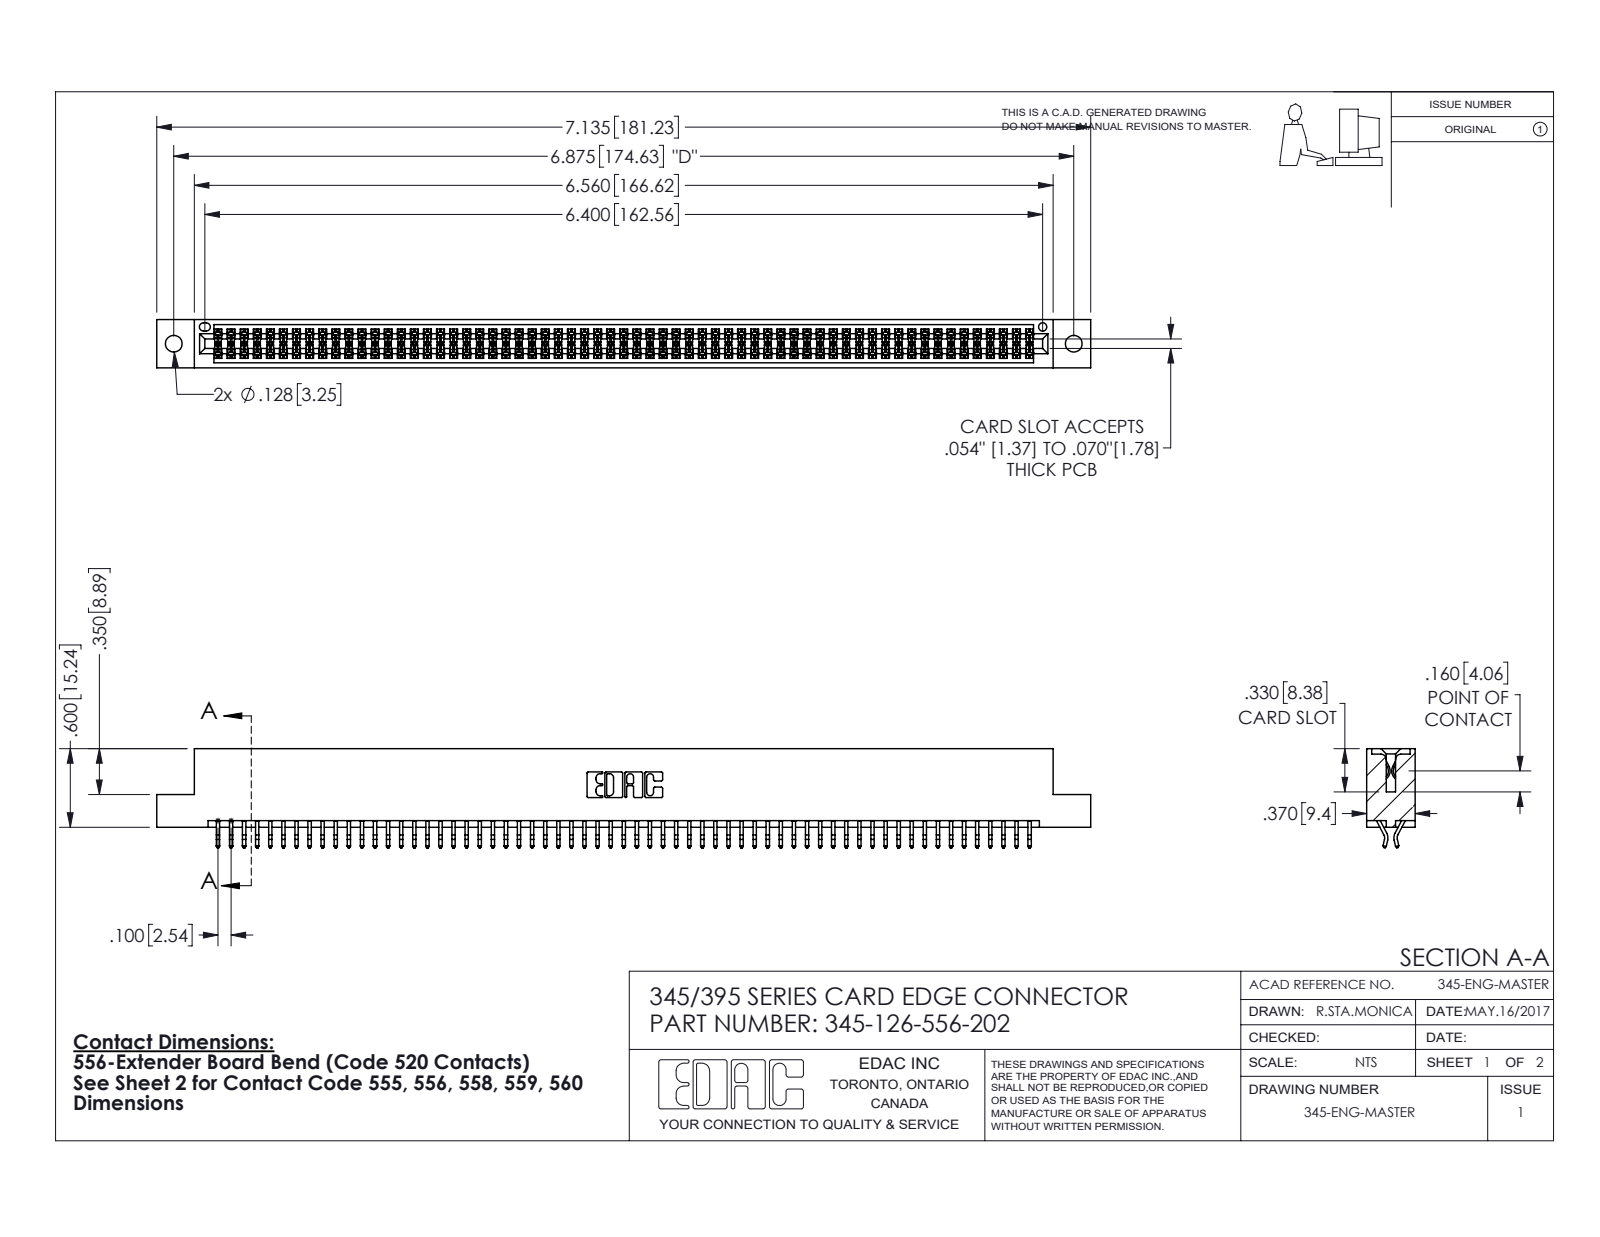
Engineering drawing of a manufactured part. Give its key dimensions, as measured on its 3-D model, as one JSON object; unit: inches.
{"part_name": "345-126-556-202; 345 Part_Flush Mounting Lugs - 0.128 Dia; 345-292-001_556 Tail", "step_written_by": "SolidWorks 2016 (CONFIG_CONTROL_DESIGN)", "units": "inches", "bodies": {"solids": 127, "faces": 7182, "planar": 4742, "cylindrical": 2440, "other": 0}, "overall_size": [7.135, 0.757, 0.37], "volume_in3": 1.084, "surface_area_in2": 40.72, "round_holes": [[0.128, 2], [0.064, 1]], "partial_cylinders_radius": [[0.006, 189], [0.01, 22], [0.007, 6], [0.031, 6], [0.026, 3], [0.01, 2], [0.014, 2], [0.019, 2]], "face_to_face_distances": [0.298, 0.072, 0.37, 0.2, 0.025, 0.098, 0.272, 0.225, 0.175, 0.149], "hole_center_spacings": [0.27, 6.639, 6.875]}
